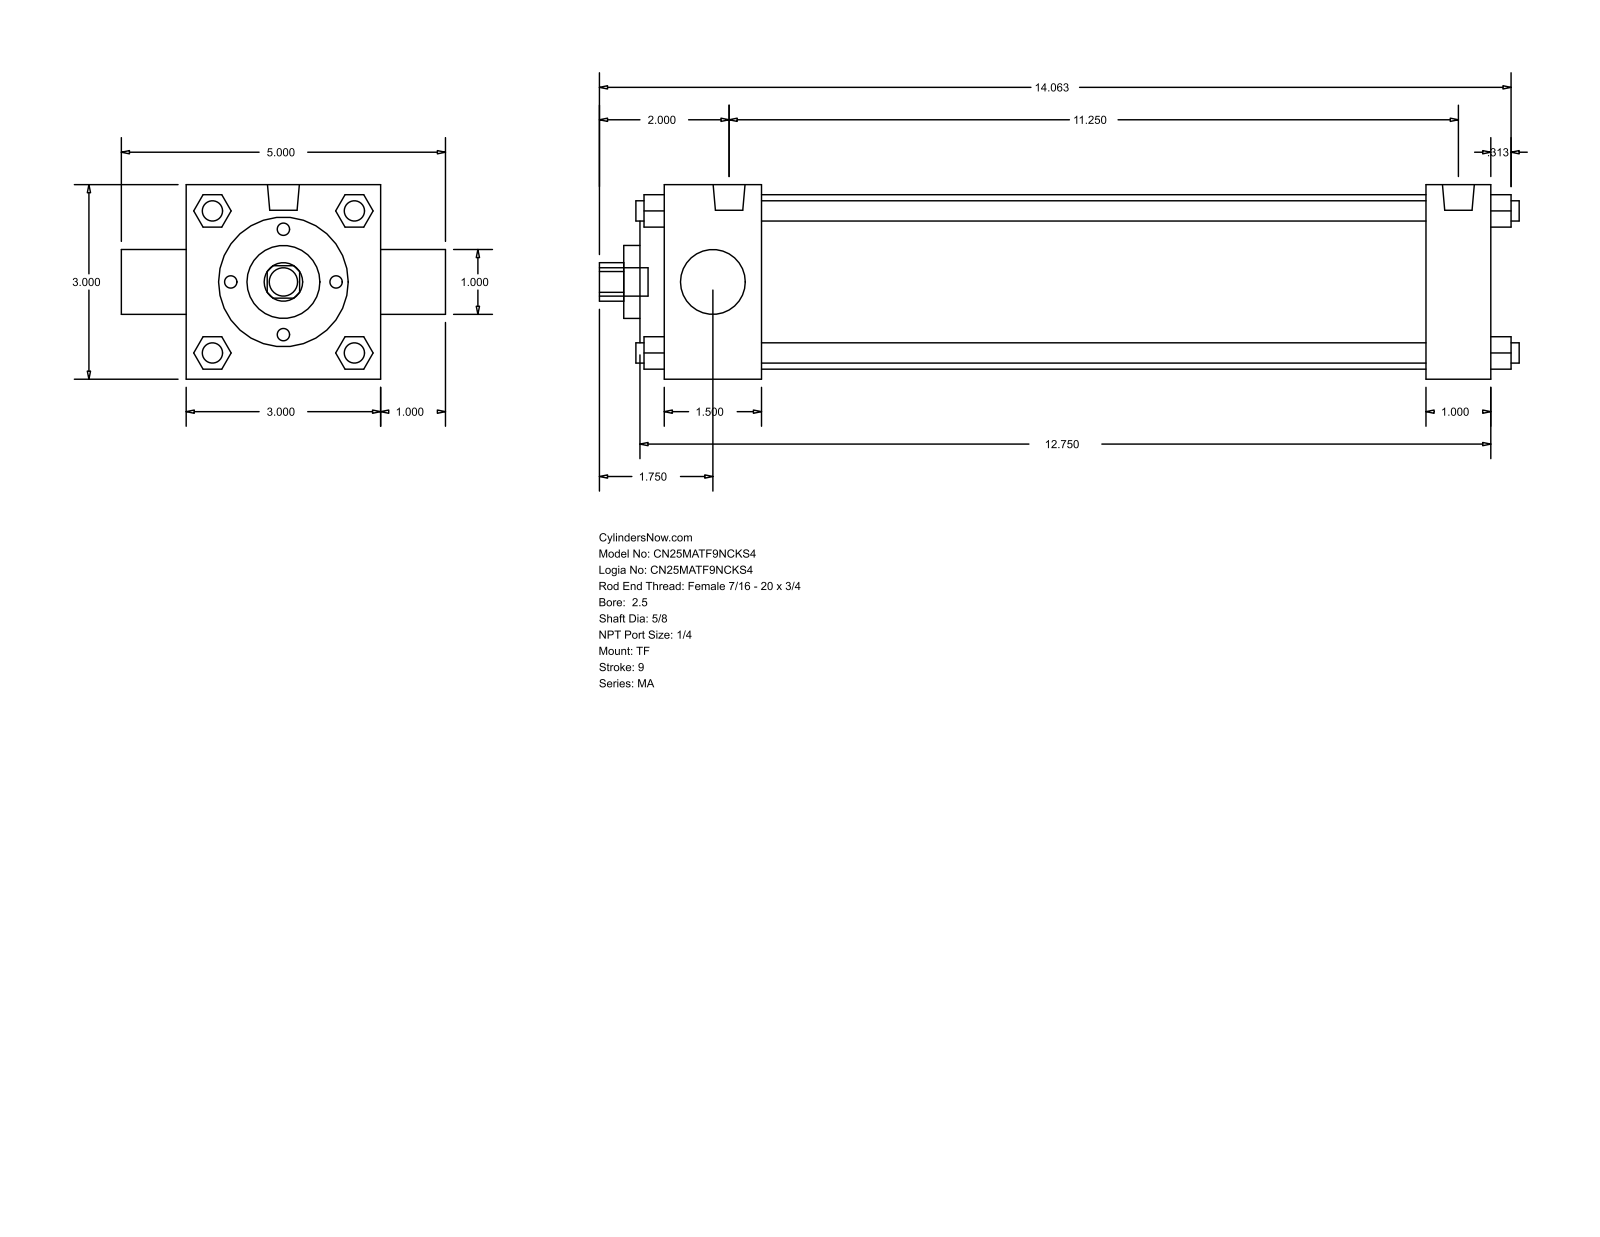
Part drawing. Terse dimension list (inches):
name: MA_TF__0250_0.625
written by: GSSL Pune (CONFIG_CONTROL_DESIGN)
unit: in
bodies: 0 solids, 122 faces (93 planar, 29 cylindrical, 0 other)
size: 14.187 × 5 × 3
holes: 1× ⌀0.625, 1× ⌀1, 1× ⌀1.125, 1× ⌀2, 1× ⌀2.69
bosses: 7× ⌀0.313, 2× ⌀0.492, 1× ⌀0.437
rounds: 1× R0.297
face distances: 3, 12.75, 1, 1.5, 11.75, 10.25, 11.25, 0.5, 0.375, 1.875
